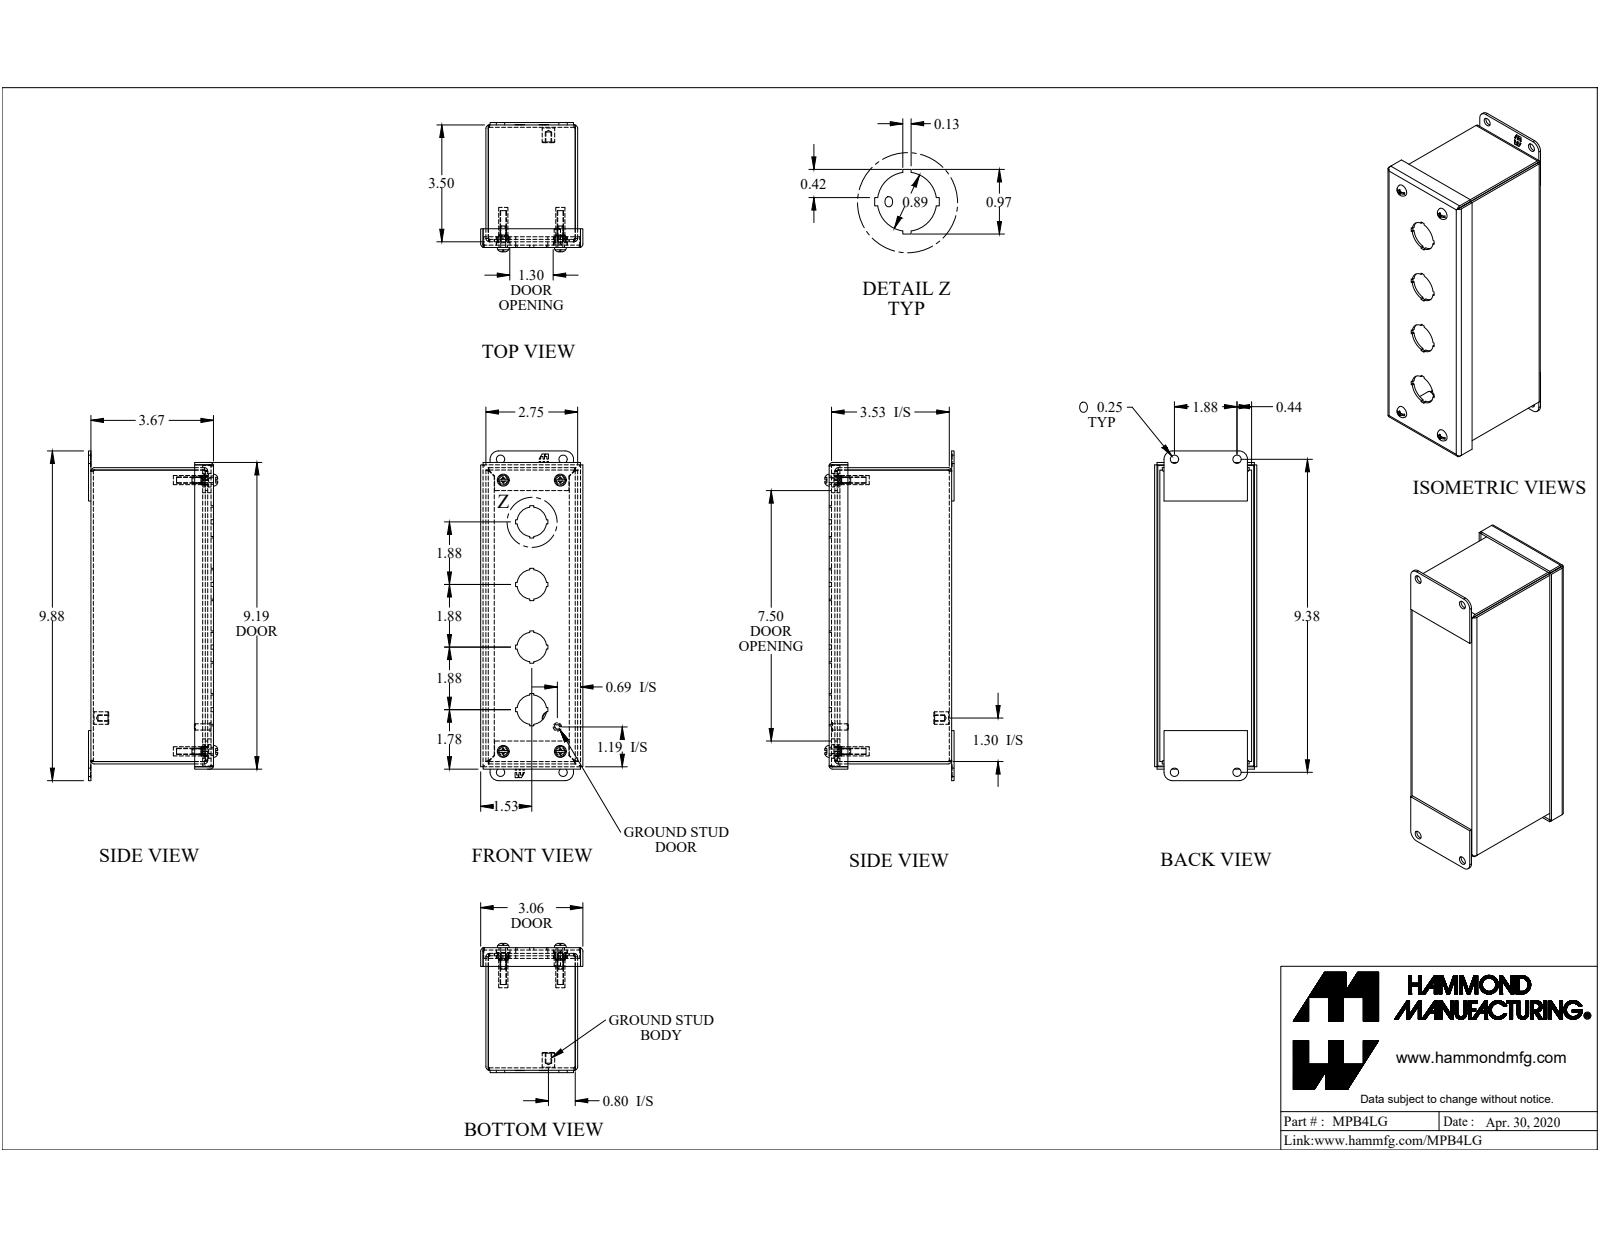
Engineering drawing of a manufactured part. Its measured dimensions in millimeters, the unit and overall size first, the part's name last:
Units: millimetres
Overall size (bounding box): 250.8 × 98.3 × 77.8
Round holes (diameter × count): ⌀6.4 ×8, ⌀4 ×4, ⌀10.3 ×4, ⌀22.5 ×4, ⌀4 ×1
Round bosses / shafts (diameter × count): ⌀9.9 ×4, ⌀7 ×4, ⌀4.8 ×4, ⌀3.8 ×4, ⌀9.5 ×1, ⌀6.4 ×1, ⌀4.8 ×1
Partial cylindrical surfaces — rounded edges, fillets, slot ends (radius × count): R0.9 ×12, R2.7 ×12, R4.1 ×4, R4.3 ×4, R6.4 ×4
Main face-to-face distances: 1.8, 1.8, 68, 91.4, 93.3, 69.9, 66.2, 89.6, 223.6, 4
Hole centre spacings: 16, 47.6, 48.2, 222.3, 226.9, 38.5, 38.5, 43.4
Volume: 218 300 mm³ · Surface area: 225 600 mm²
Bodies: 19 solids, 555 faces (407 planar, 112 cylindrical, 36 other)
Part name (STEP PRODUCT): MPB4LG
STEP written by: SolidWorks 2019 (AUTOMOTIVE_DESIGN)
